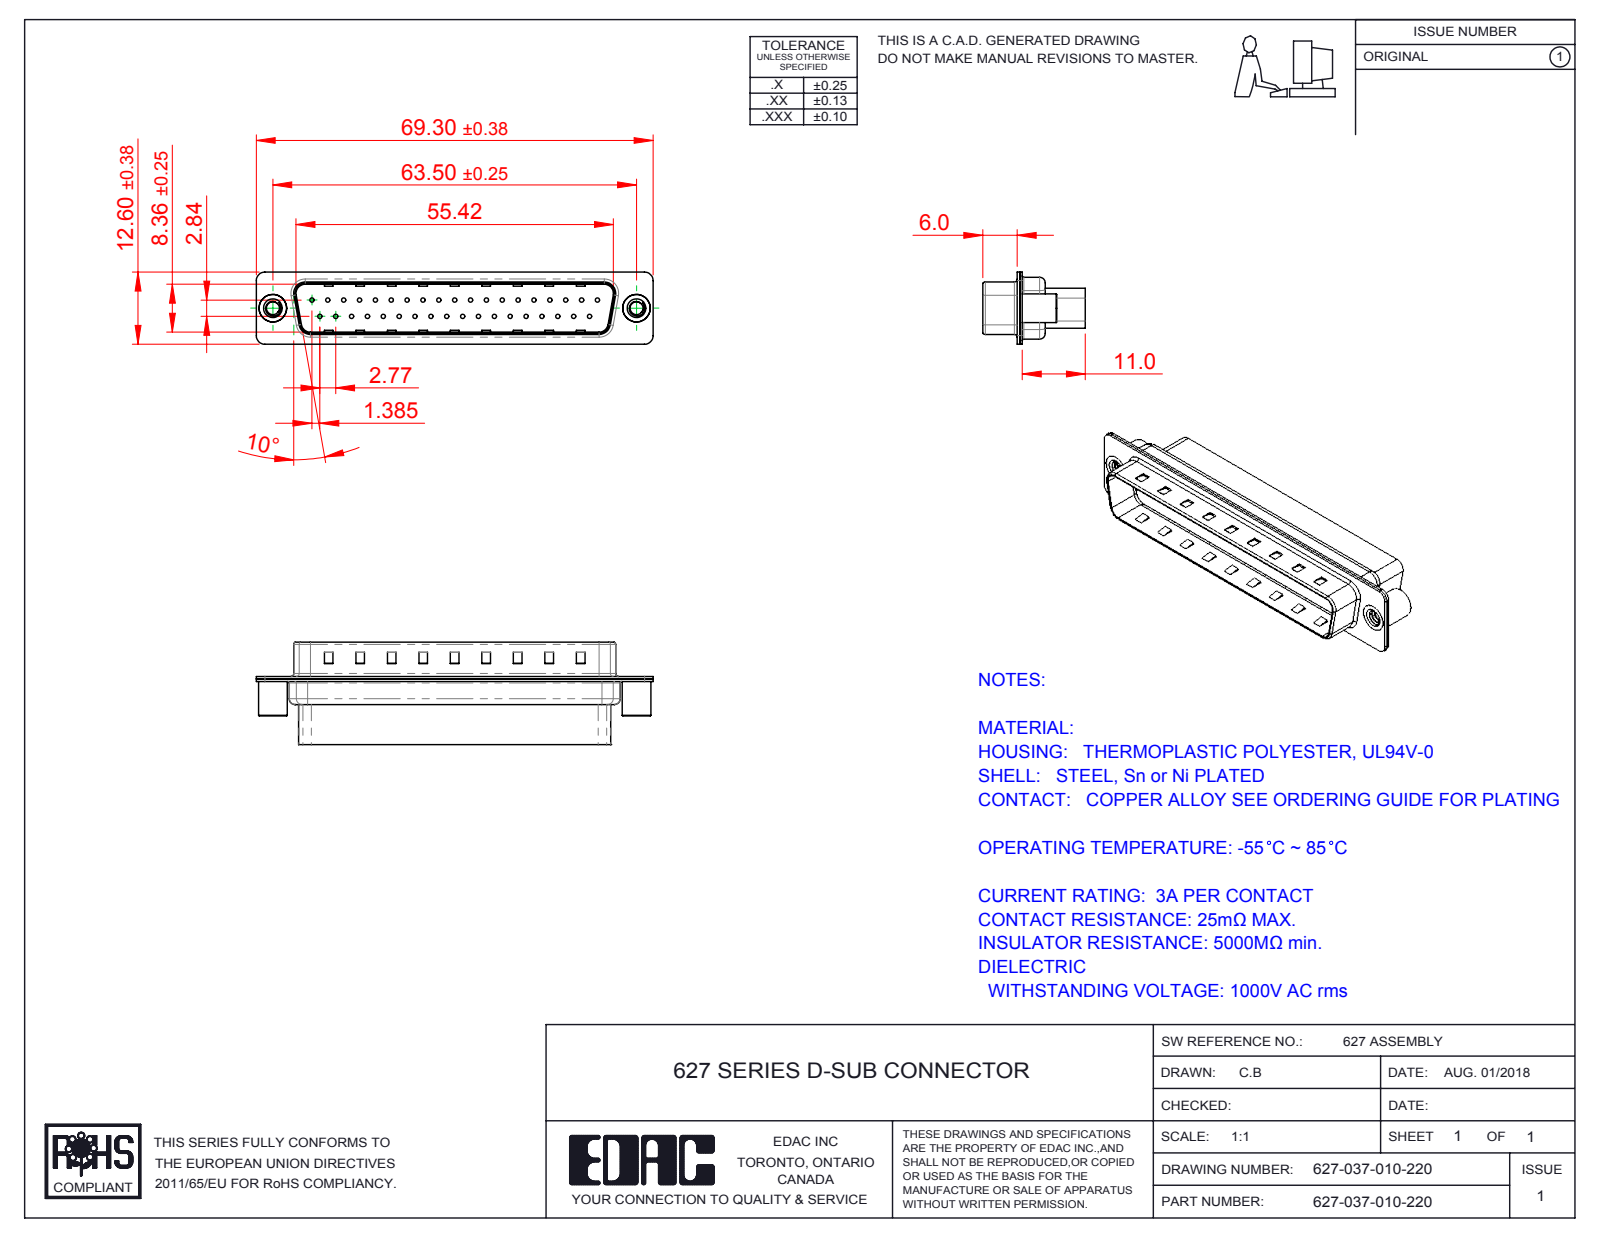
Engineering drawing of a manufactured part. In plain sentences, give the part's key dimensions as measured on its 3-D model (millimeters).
The part is named "627 Shell Rear_37 Contacts; 627 Shell Front_37 Contacts; 627 Housing_37 HP; 627 4-40 Threaded Standoff BS (+1 more)". Its 3-D file was written by "SolidWorks 2016 (CONFIG_CONTROL_DESIGN)". It is 5 solids with 730 faces: 277 planar, 383 cylindrical and 70 other. Overall it measures 69.3 by 17.9 by 12.6 millimeters. Its volume is 5 120 cubic millimeters and its surface area 9 227 square millimeters. Round holes: 37 of diameter 0.75, 37 of diameter 1.6, 37 of diameter 2, 2 of diameter 2.26, 2 of diameter 4, 2 of diameter 4.8. Round bosses or shafts: 2 of diameter 5, 2 of diameter 4.9. Partial cylindrical surfaces (rounded edges, fillets, slot ends): 16 of radius 1.5, 12 of radius 2, 8 of radius 0.5, 8 of radius 1.6, 4 of radius 0.25, 4 of radius 0.6, 4 of radius 0.65, 4 of radius 0.9. The main face-to-face distances are 0.4, 0.82, 9.58, 0.68, 7.68, 0.45, 1.08, 8.08, 8.76, 7. The hole center spacings are 3.16, 2.77, 5.54, 8.31, 5.04, 10.1, 11.08, 12.78.
